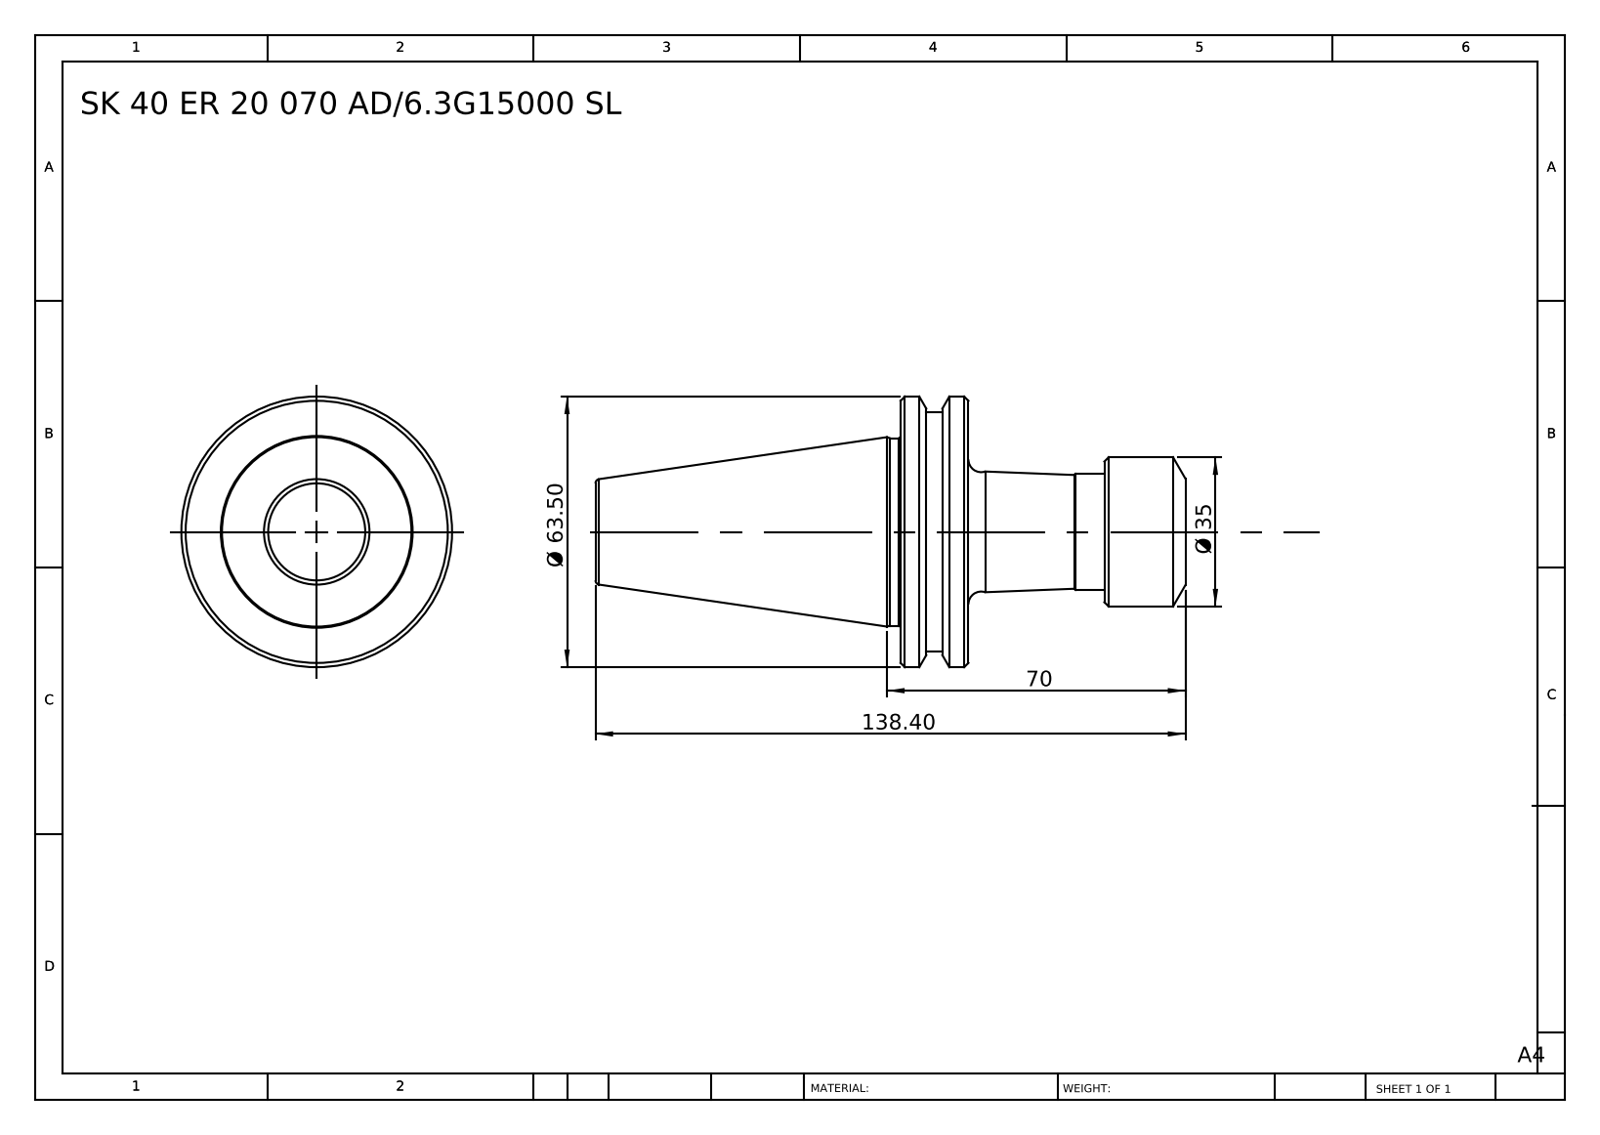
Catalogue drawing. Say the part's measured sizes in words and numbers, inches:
The part is named "SK 40 ER 20 070 AD-6.3G15000 SL". Its 3-D file was written by "SolidWorks 2014 (CONFIG_CONTROL_DESIGN)". It is 1 solid with 47 faces: 7 planar, 12 cylindrical and 28 other. Overall it measures 5.449 by 2.5 by 2.5 inches. Its volume is 9.382 cubic inches and its surface area 34.26 square inches. Round bosses or shafts: 1 of diameter 2.5, 1 of diameter 2.205, 1 of diameter 1.732, 1 of diameter 1.378, 1 of diameter 1.07. The main face-to-face distances are 0.626, 2.004, 2.63, 5.449, 3.445, 2.819, 0.748, 1.256, 1.882, 4.701.
